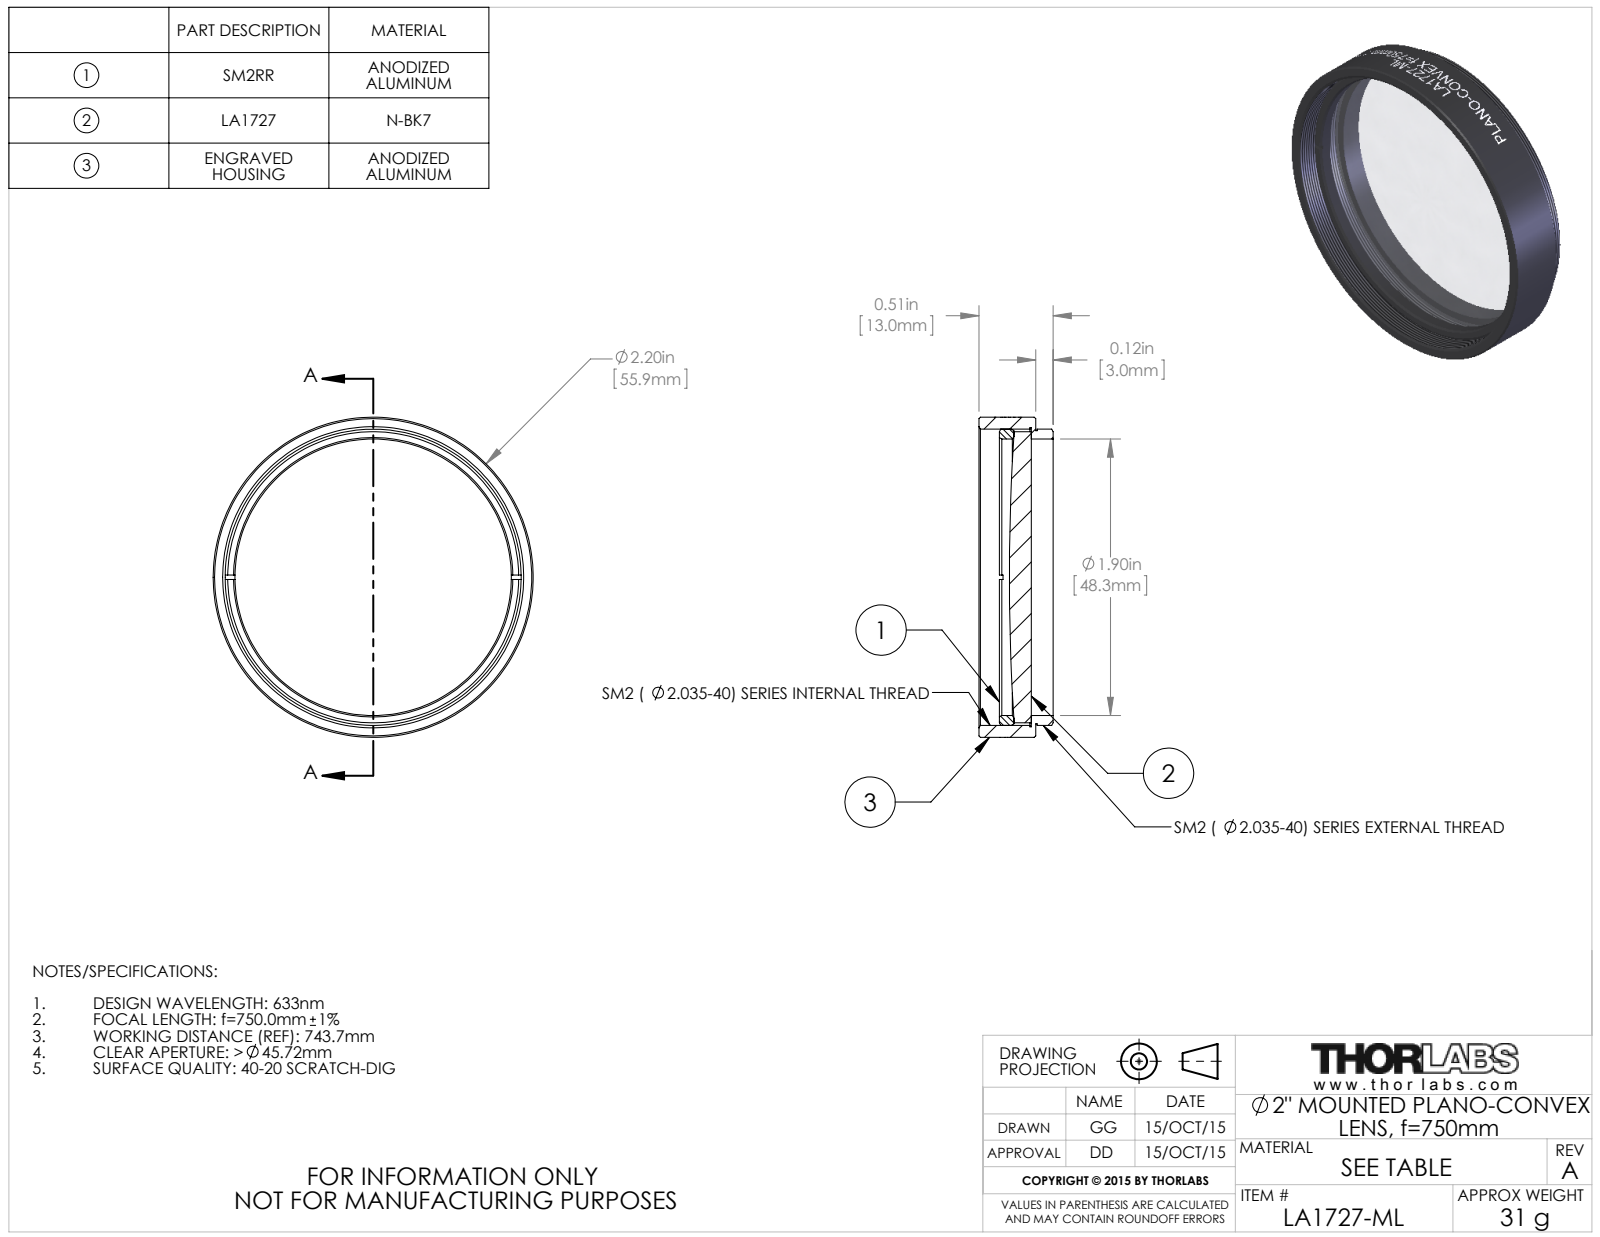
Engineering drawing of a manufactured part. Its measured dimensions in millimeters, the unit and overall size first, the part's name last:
Units: millimetres
Overall size (bounding box): 55.9 × 55.9 × 13
Round holes (diameter × count): ⌀48.3 ×1, ⌀52.2 ×1
Round bosses / shafts (diameter × count): ⌀55.9 ×1, ⌀51.7 ×1, ⌀51.2 ×1, ⌀50.8 ×1
Main face-to-face distances: 3, 3.8, 0.8, 9.9, 9.1, 13, 6.9, 6.1, 9.4, 6.4
Volume: 12 000 mm³ · Surface area: 11 350 mm²
Bodies: 3 solids, 106 faces (16 planar, 70 cylindrical, 20 other)
Part name (STEP PRODUCT): TTN039618-E0W
STEP written by: SolidWorks 2014 (CONFIG_CONTROL_DESIGN)
